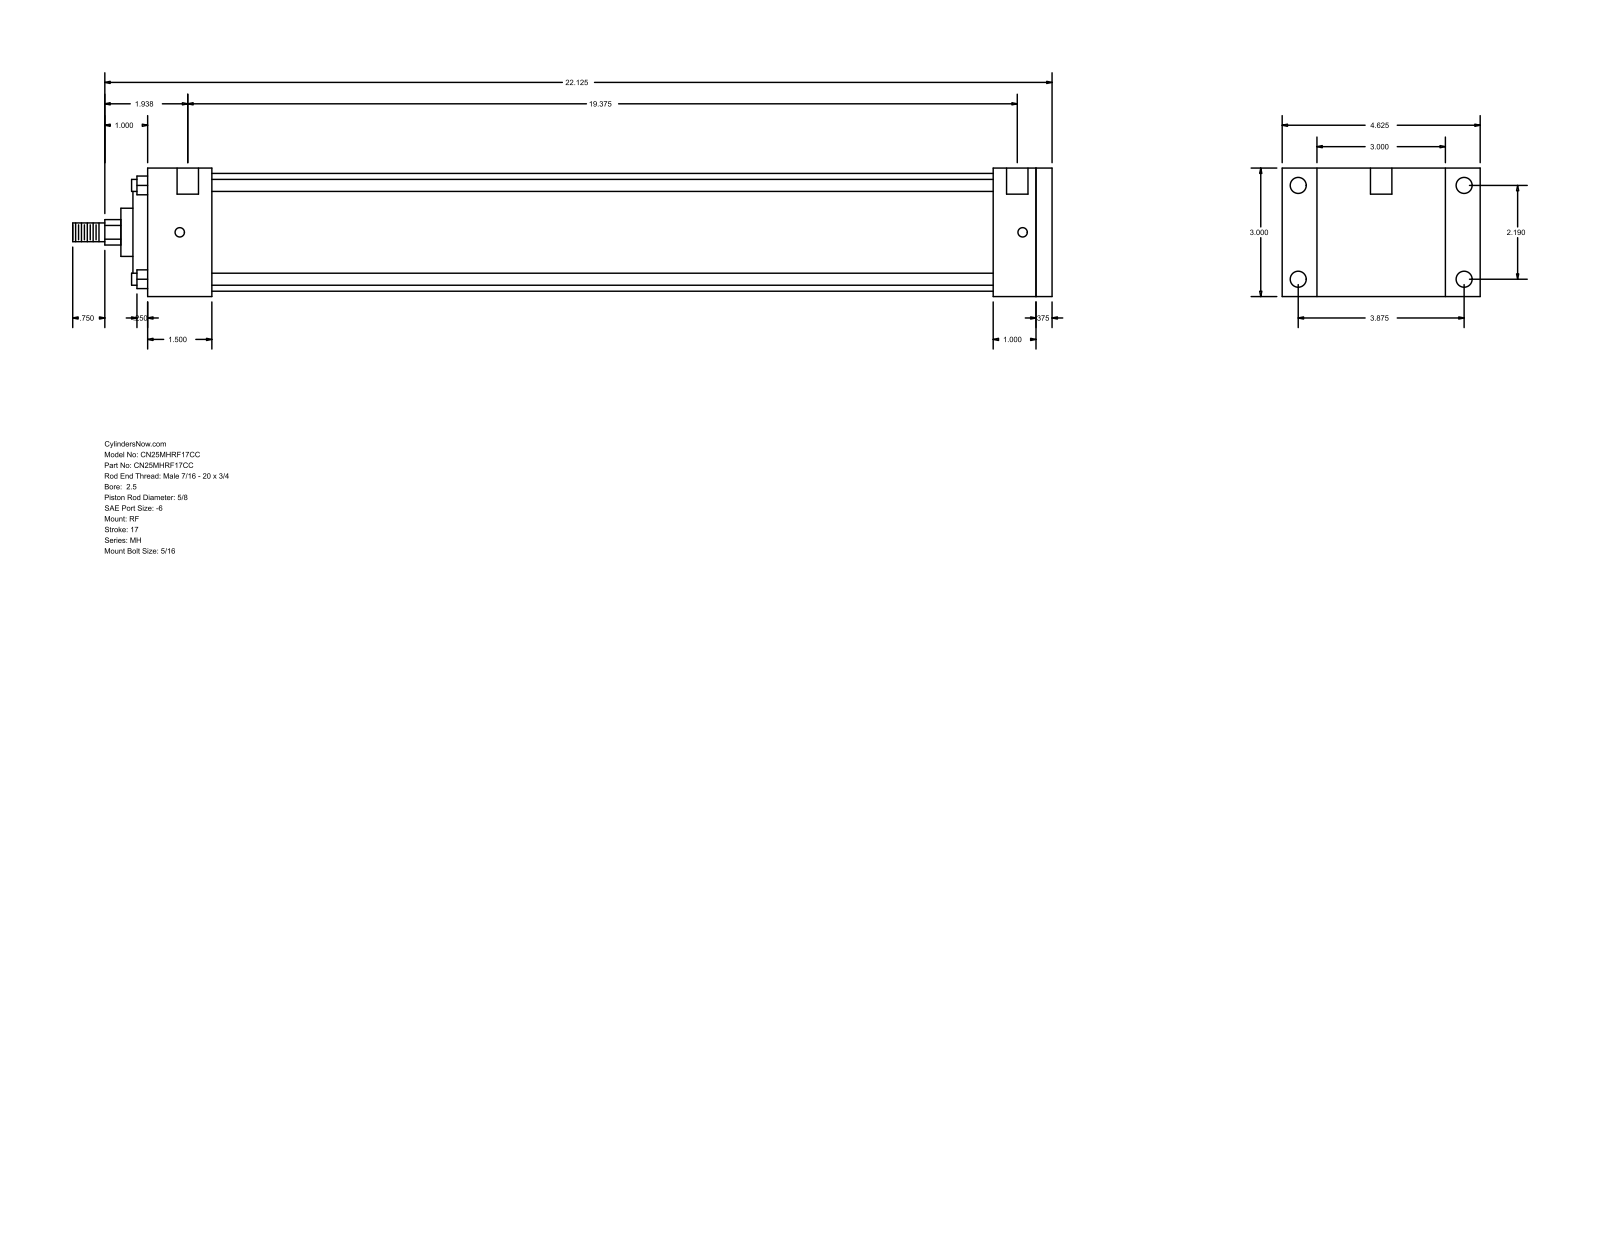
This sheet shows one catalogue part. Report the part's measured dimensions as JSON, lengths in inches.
{"part_name": "MH_RF__0250_0.625", "step_written_by": "GSSL Pune (CONFIG_CONTROL_DESIGN)", "units": "inches", "bodies": {"solids": 0, "faces": 94, "planar": 65, "cylindrical": 29, "other": 0}, "overall_size": [22.875, 4.625, 3], "round_holes": [[0.219, 4], [0.375, 4], [0.5, 2]], "round_bosses_or_shafts": [[0.281, 4], [2.75, 1], [2.187, 1], [1.125, 1], [0.625, 1], [0.437, 1]], "partial_cylinders_radius": [[0.297, 1]], "face_to_face_distances": [3, 0.375, 21.125, 20.75, 1, 1.375, 1.5, 19.75, 18.25, 19.25], "hole_center_spacings": [2.19, 3.875, 4.451, 19.687, 0.125, 0.187, 19.375, 19.5]}
